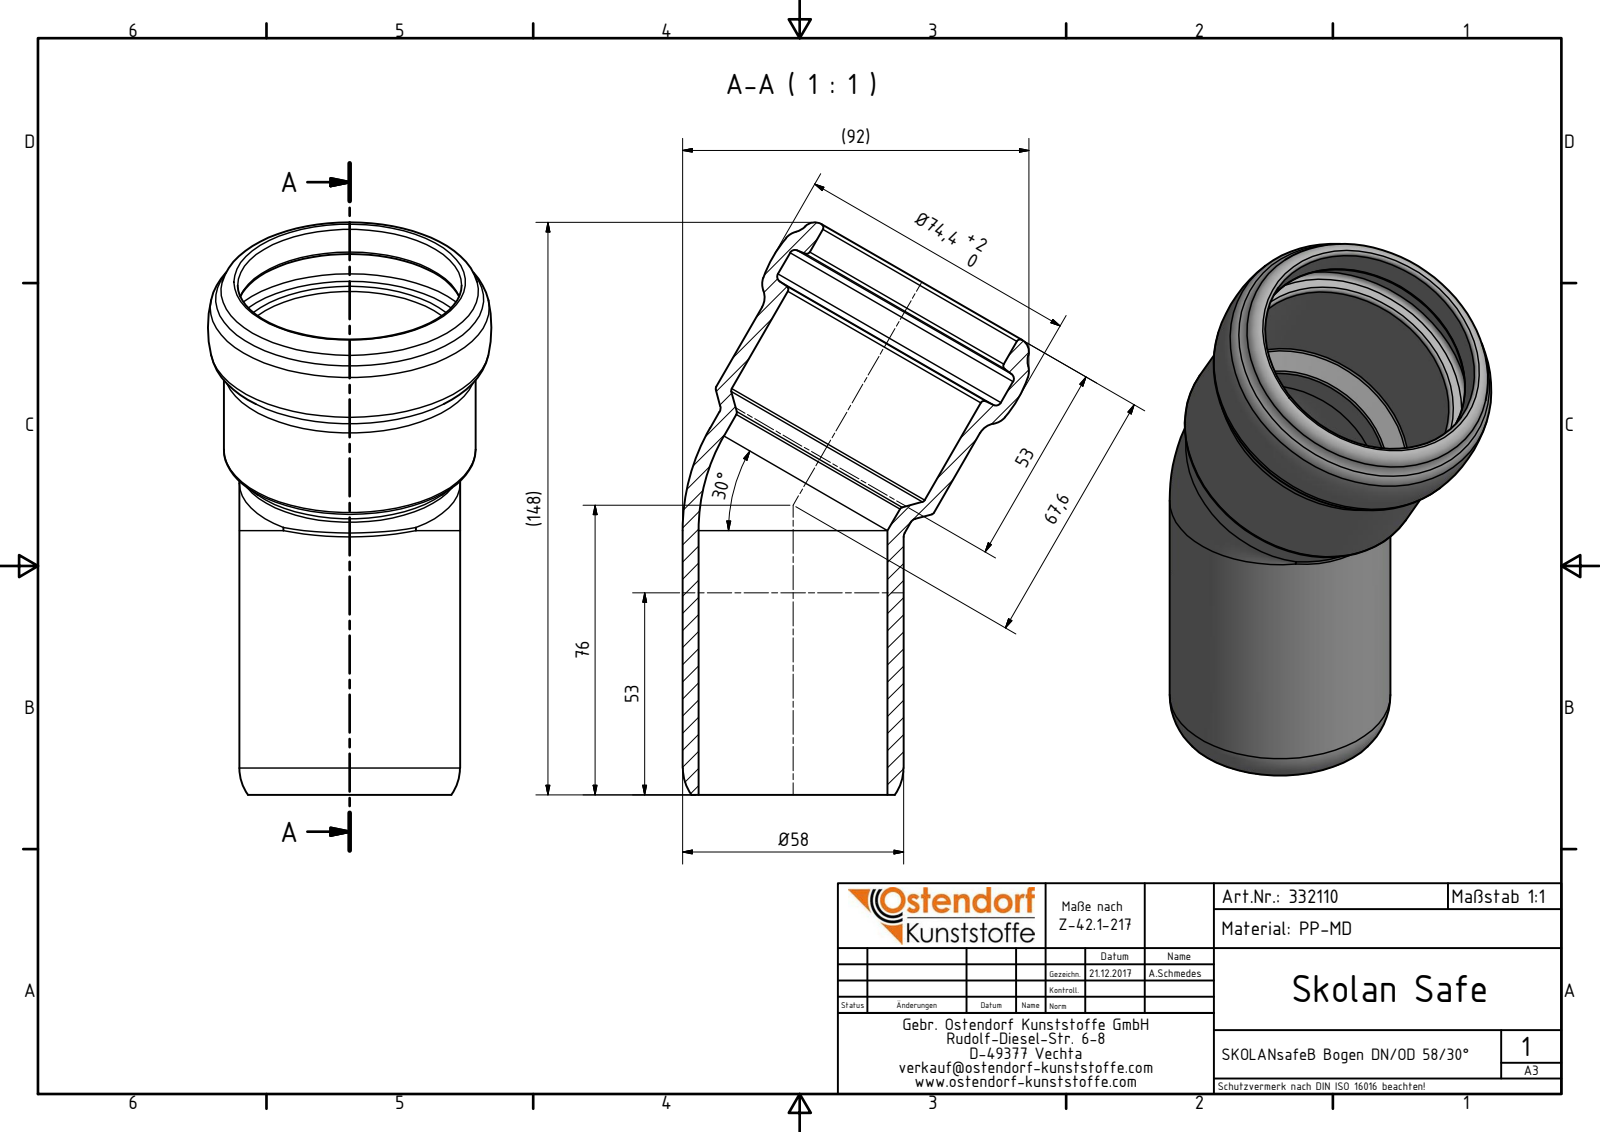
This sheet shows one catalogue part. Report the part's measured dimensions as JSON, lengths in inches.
{"part_name": "332110 SKOLANsafeB Bogen DN_OD 58_30°", "step_written_by": "Autodesk Inventor 2016 (AUTOMOTIVE_DESIGN)", "units": "inches", "bodies": {"solids": 1, "faces": 32, "planar": 1, "cylindrical": 8, "other": 23}, "overall_size": [5.914, 3.58, 2.929], "volume_in3": 6.714, "surface_area_in2": 85.47, "round_holes": [[1.953, 2], [2.303, 1], [2.315, 1], [2.661, 1]], "round_bosses_or_shafts": [[2.283, 2], [2.602, 1]]}
